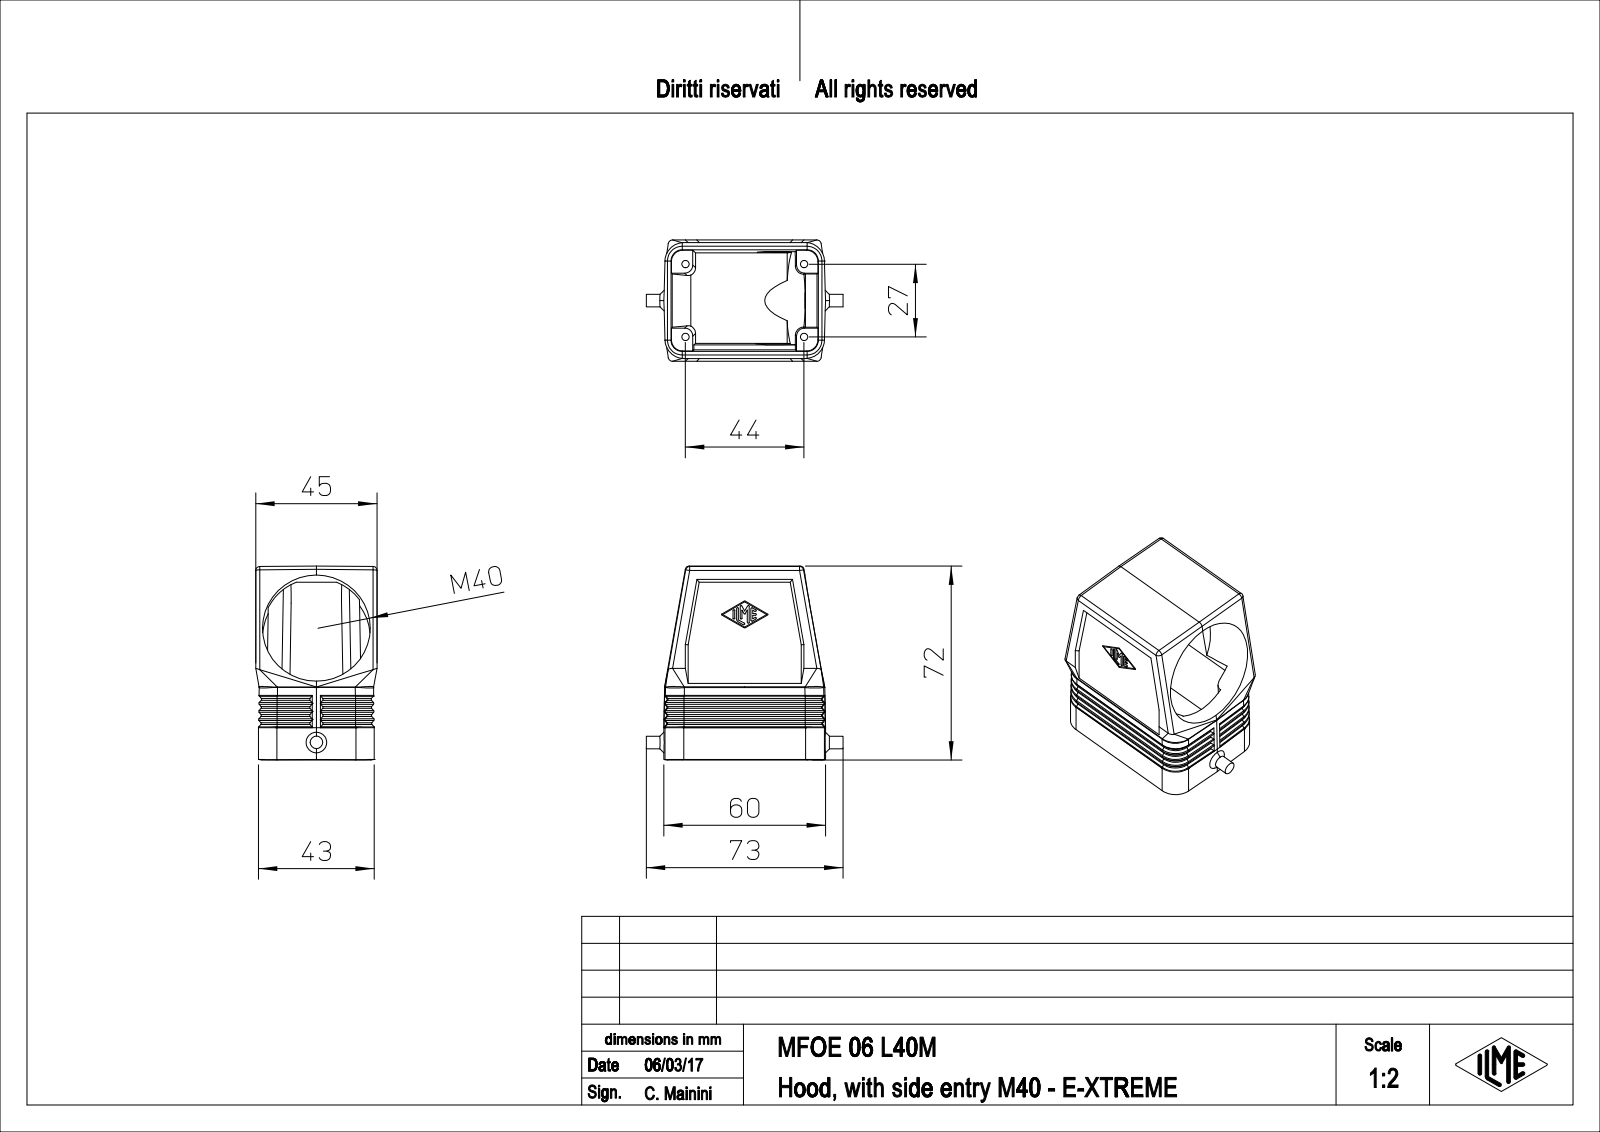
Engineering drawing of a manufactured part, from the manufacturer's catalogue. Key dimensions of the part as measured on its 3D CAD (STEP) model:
Part name (STEP PRODUCT): MFOE_06_L40M
STEP written by: PTC Creo Elements/Direct Modeling 19.0E 27-Jun-2016 (C) Parametric Technology GmbH (AUTOMOTIVE_DESIGN)
Units: millimetres
Bodies: 1 solid, 384 faces (158 planar, 102 cylindrical, 124 other)
Overall size (bounding box): 73 × 72 × 45
Volume: 52 544 mm³ · Surface area: 27 963 mm²
Round holes (diameter × count): ⌀2.75 ×4, ⌀40 ×1
Round bosses / shafts (diameter × count): ⌀4.62 ×1
Partial cylindrical surfaces — rounded edges, fillets, slot ends (radius × count): R0.5 ×54, R1.5 ×10, R7 ×8, R3 ×4, R4.2 ×4
Main face-to-face distances: 43, 1.85, 7.95, 2, 1, 44, 8.5, 4, 45, 60
Hole centre spacings: 27, 44, 51.62
